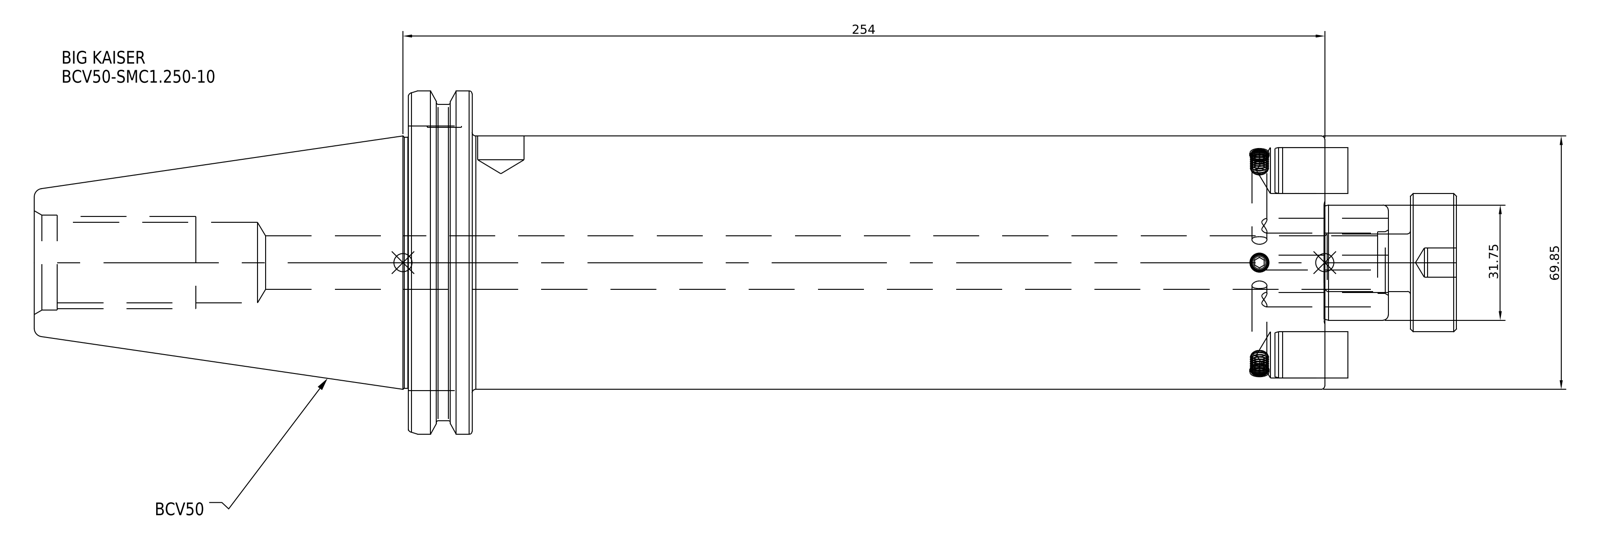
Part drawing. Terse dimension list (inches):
name: BCV50-SMC1_250-10
written by: SolidWorks 2021 (CONFIG_CONTROL_DESIGN)
unit: in
bodies: 1 solid, 35 faces (17 planar, 12 cylindrical, 6 other)
size: 14.252 × 3.875 × 3.875
volume: 76.1 in³; area: 154.7 in²
holes: 1× ⌀0.578
bosses: 1× ⌀3.875, 1× ⌀3.594, 1× ⌀2.75
face distances: 0.691, 9.25, 9.941, 14, 4.75, 4.059, 0.5, 0.252, 9.502, 10.193
